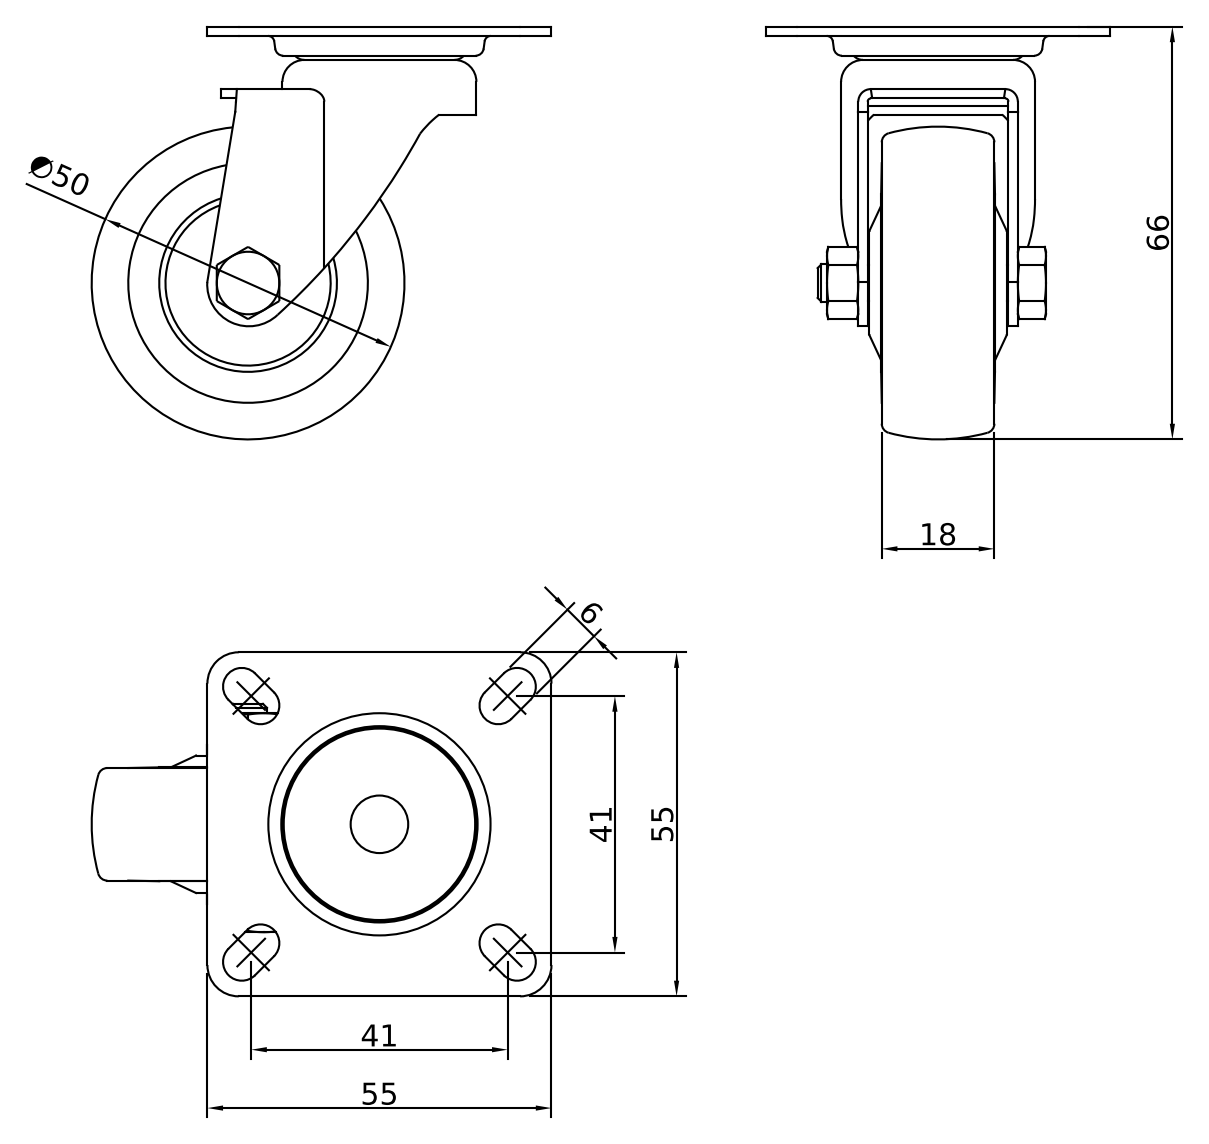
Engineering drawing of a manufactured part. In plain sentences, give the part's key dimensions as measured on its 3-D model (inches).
The part is named "CRUST0000176; 440000025234; 440000025235; 440000025236 (+3 more)". Its 3-D file was written by "Autodesk Inventor 2022 (AUTOMOTIVE_DESIGN)". It is 7 solids with 191 faces: 64 planar, 46 cylindrical and 81 other. Overall it measures 2.894 by 2.598 by 2.165 inches. Its volume is 2.59 cubic inches and its surface area 41.85 square inches. Round holes: 1 of diameter 0.194, 1 of diameter 0.236, 1 of diameter 0.248, 1 of diameter 0.315, 1 of diameter 0.362, 1 of diameter 0.638, 1 of diameter 1, 1 of diameter 1.102, 1 of diameter 1.118. Round bosses or shafts: 1 of diameter 1.22, 1 of diameter 1.039, 1 of diameter 1.024, 1 of diameter 0.748, 1 of diameter 0.311, 1 of diameter 0.232. Partial cylindrical surfaces (rounded edges, fillets, slot ends): 8 of radius 0.118, 4 of radius 0.197, 2 of radius 0.02, 2 of radius 0.079, 1 of radius 0.263, 1 of radius 0.664, 1 of radius 0.973, 1 of radius 4.416. The main face-to-face distances are 0.059, 0.089, 0.856, 0.945, 0.148, 0.797, 0.394, 0.915, 0.03, 0.768.
